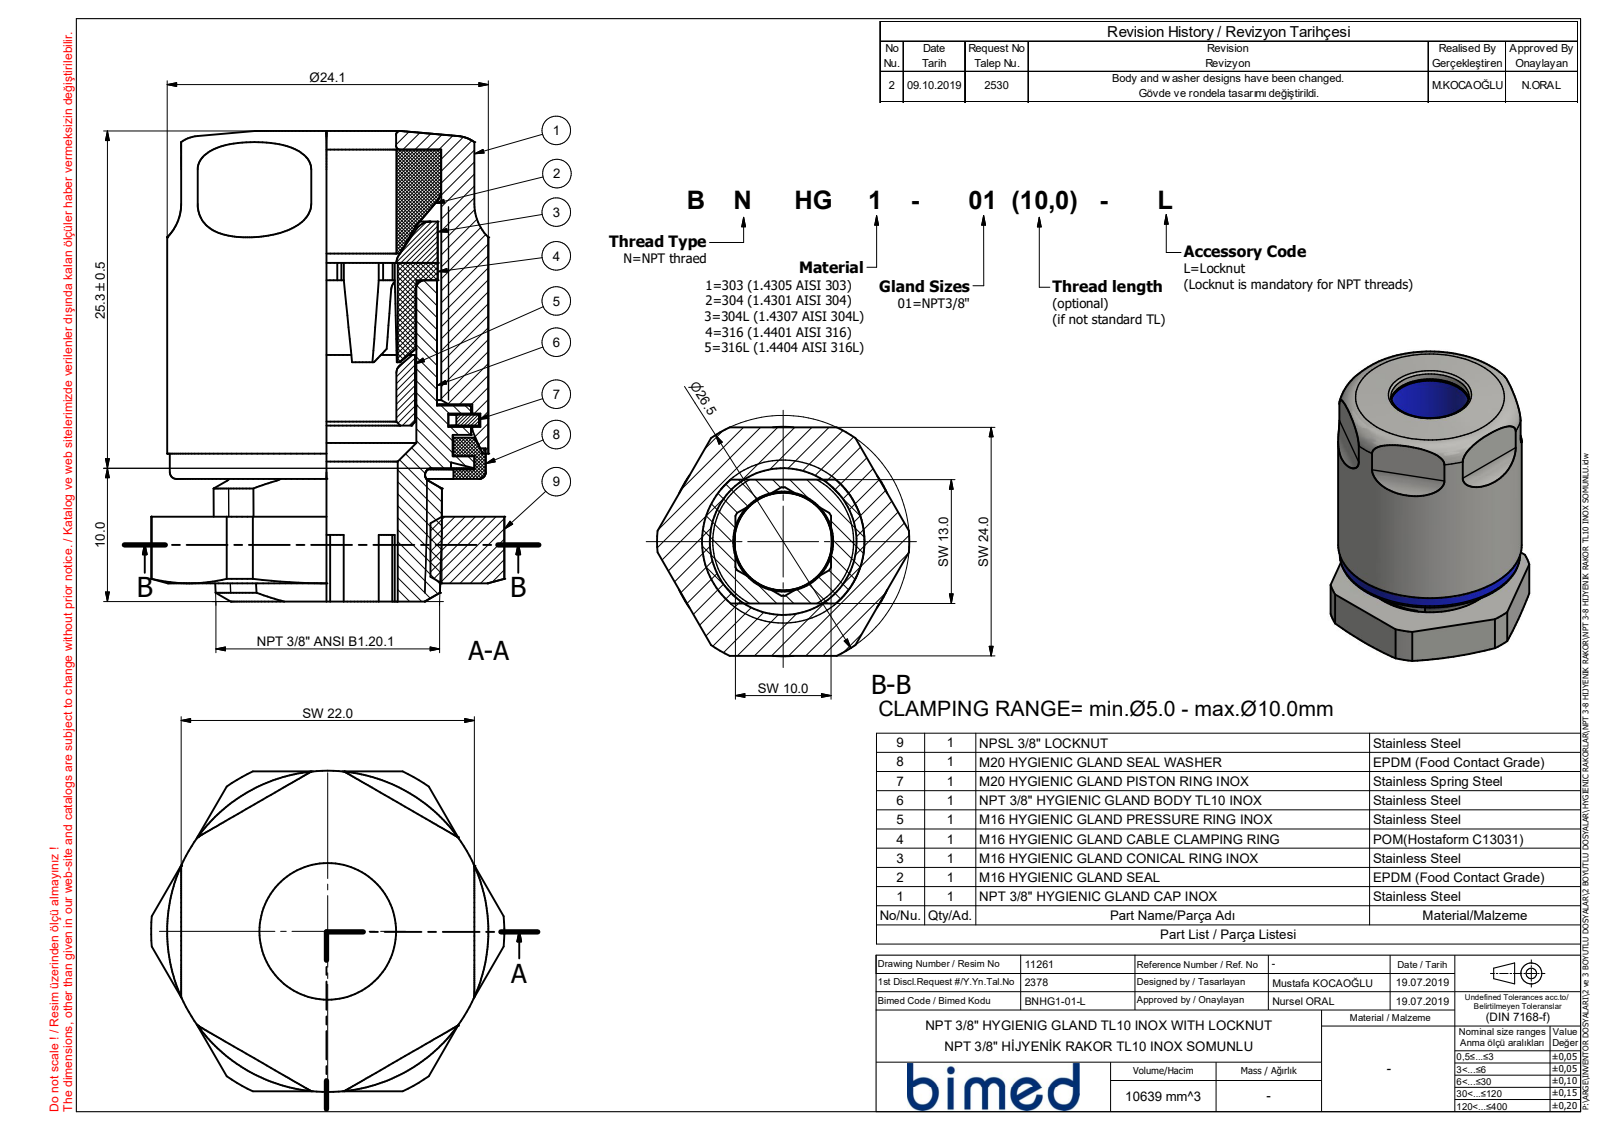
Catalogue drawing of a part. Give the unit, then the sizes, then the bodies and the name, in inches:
Units: inches
Overall size (bounding box): 1.409 × 1.043 × 0.949
Round bosses / shafts (diameter × count): ⌀0.949 ×1, ⌀0.933 ×1
Partial cylindrical surfaces — rounded edges, fillets, slot ends (radius × count): R0.522 ×1
Main face-to-face distances: 0.197, 0.309, 0.112, 0.945, 0.054, 0.25, 0.362, 0.217, 0.728, 0.512
Volume: 0.913 in³ · Surface area: 6.197 in²
Bodies: 1 solid, 57 faces (15 planar, 10 cylindrical, 32 other)
Part name (STEP PRODUCT): BNHG1-01-L
STEP written by: SolidWorks 2021 (CONFIG_CONTROL_DESIGN)
